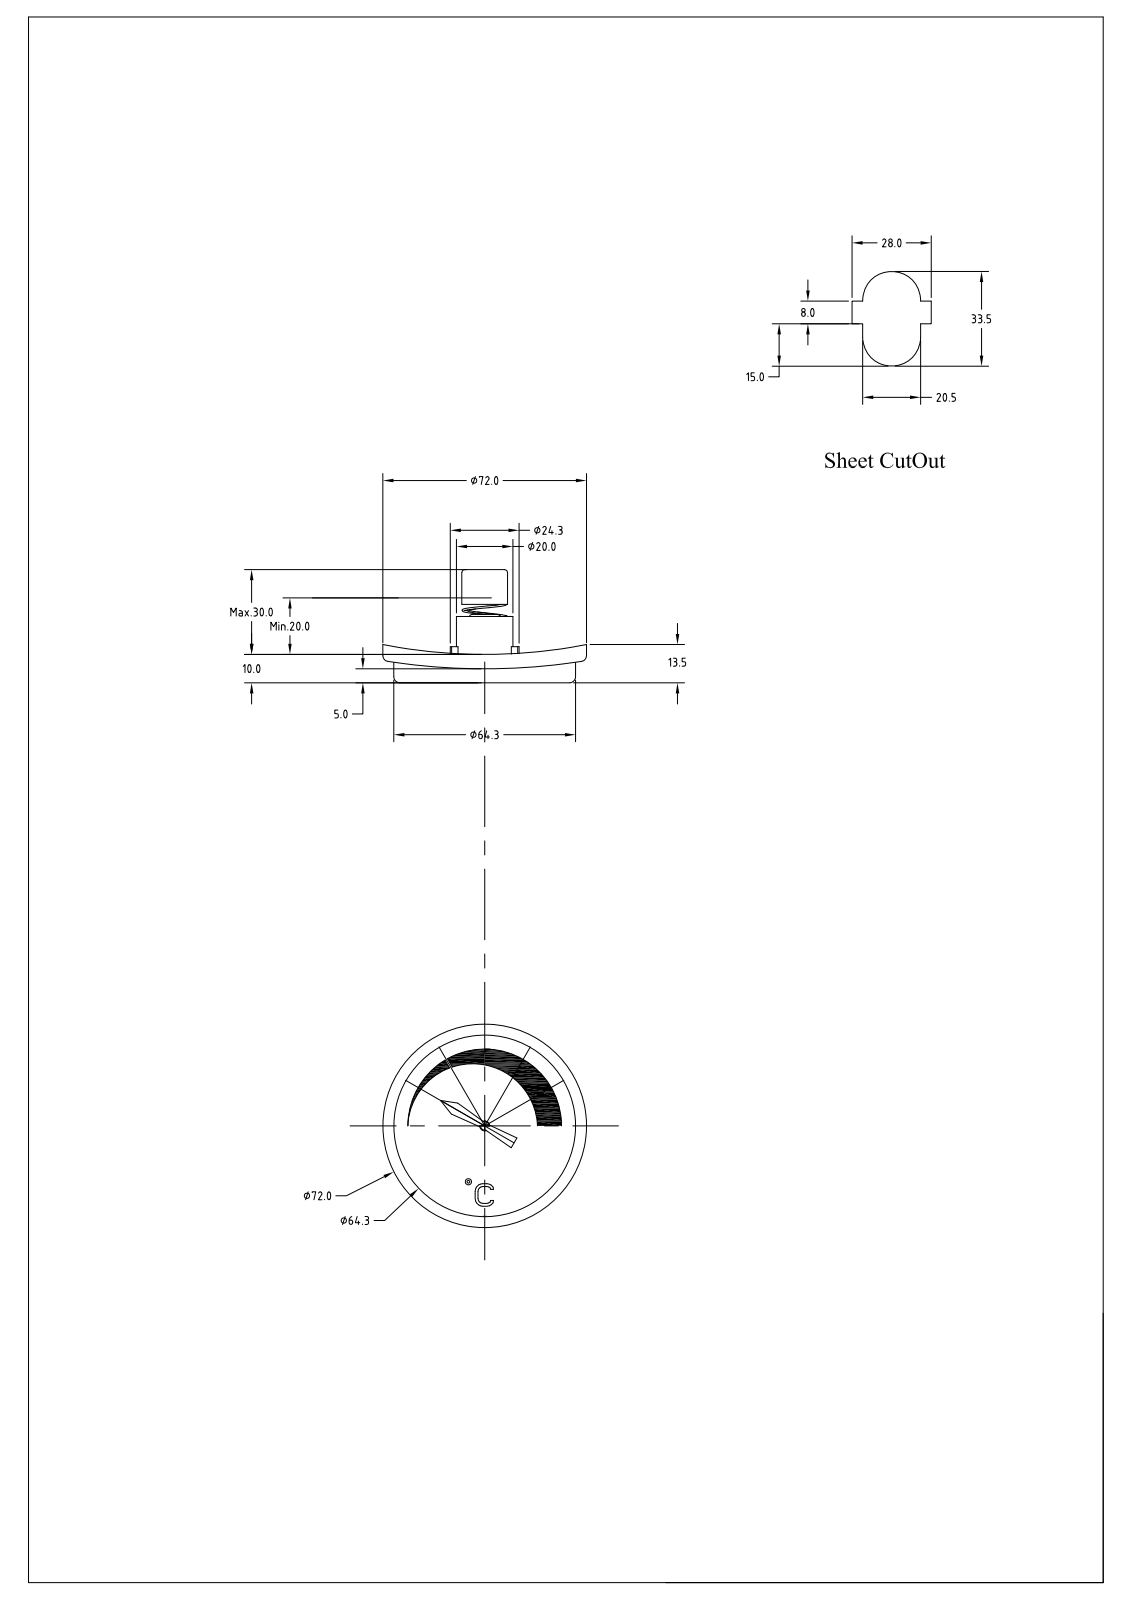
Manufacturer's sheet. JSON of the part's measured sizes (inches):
{"part_name": "EWH-THERMOMETER-A_ASM_ASM", "step_written_by": "CREO PARAMETRIC BY PTC INC, 2024063 (CONFIG_CONTROL_DESIGN)", "units": "inches", "bodies": {"solids": 1, "faces": 23, "planar": 4, "cylindrical": 10, "other": 9}, "overall_size": [2.835, 2.835, 1.557], "volume_in3": 2.667, "surface_area_in2": 18.62, "round_bosses_or_shafts": [[2.835, 1], [2.512, 1], [0.787, 1], [0.636, 1]], "partial_cylinders_radius": [[8.661, 1], [8.858, 1]], "face_to_face_distances": [0.915, 0.169, 1.085, 0.472, 0.642, 1.557]}
